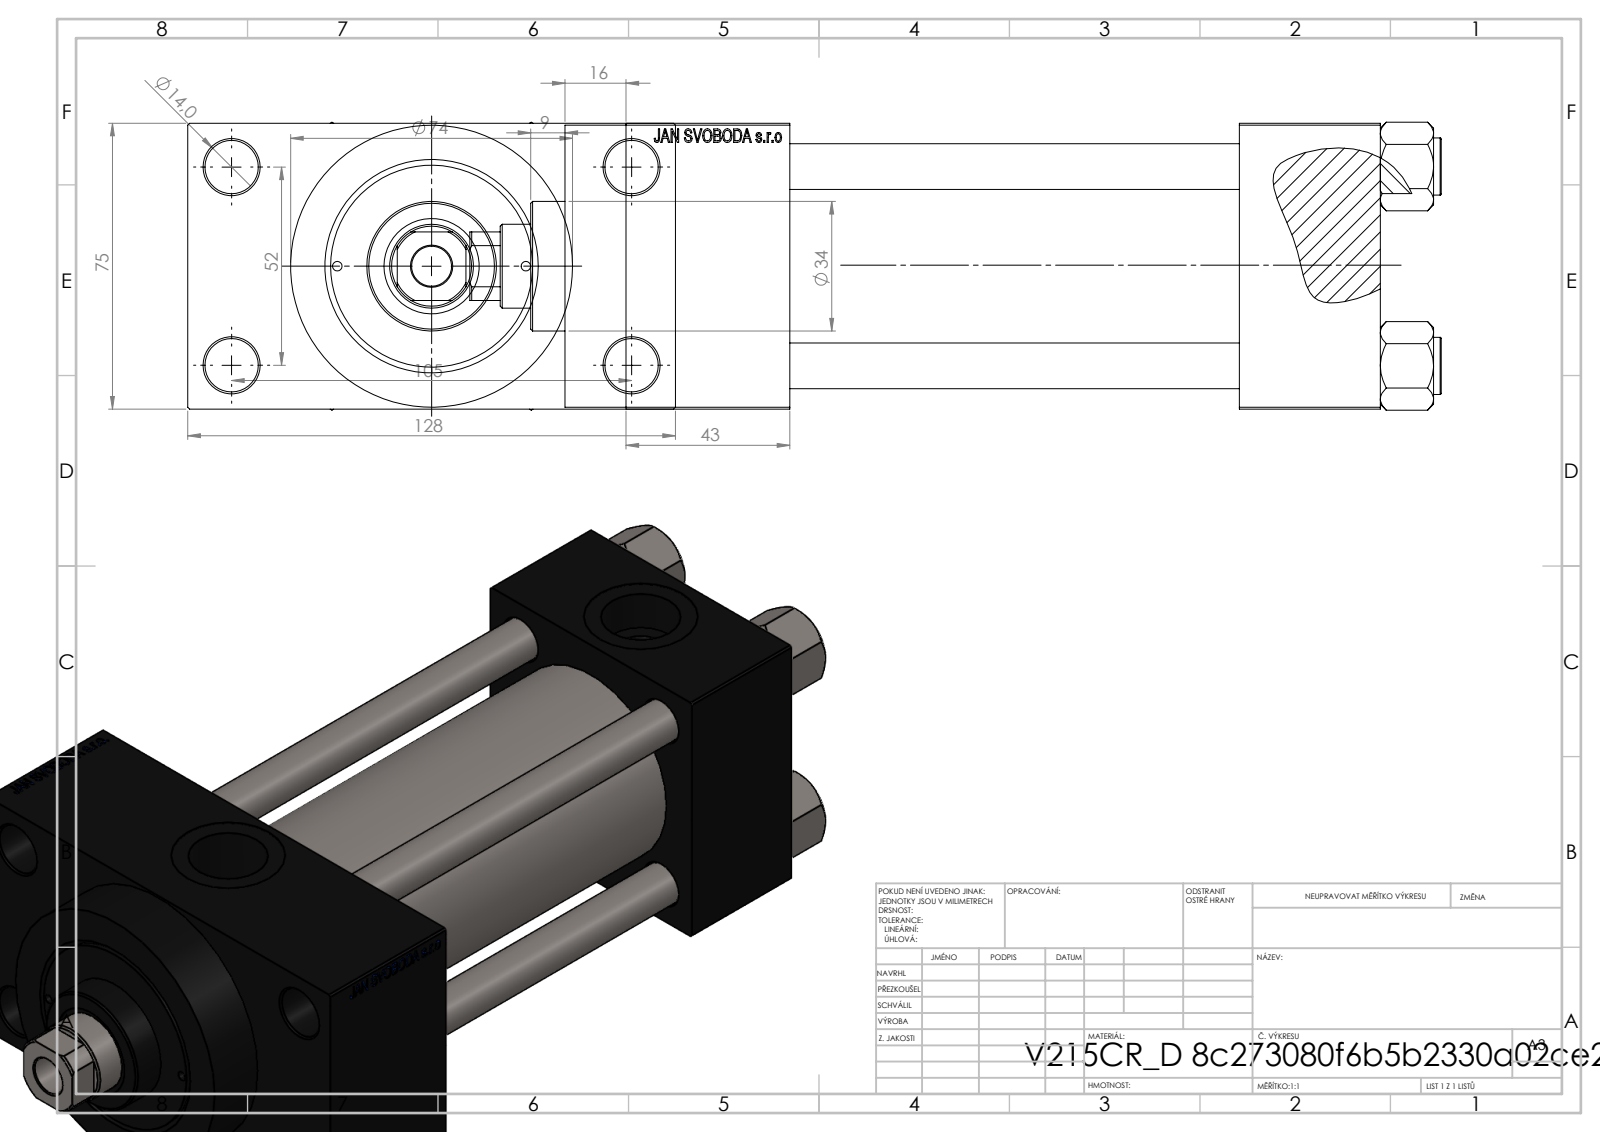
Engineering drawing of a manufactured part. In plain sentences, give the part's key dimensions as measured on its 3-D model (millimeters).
The part is named "V215CR_D_Body; V215CR_VCP_D; NUT_M5_D; V215_VC_A (+1 more)". Its 3-D file was written by "SolidWorks 2019 (CONFIG_CONTROL_DESIGN)". It is 11 solids with 1112 faces: 499 planar, 93 cylindrical and 520 other. Overall it measures 255 by 128 by 75.54 millimeters. Its volume is 886 222 cubic millimeters and its surface area 198 058 square millimeters. Round holes: 4 of diameter 12, 4 of diameter 14, 2 of diameter 2.5, 2 of diameter 7, 2 of diameter 20.96, 2 of diameter 30, 1 of diameter 10.5, 1 of diameter 22, 1 of diameter 25, 1 of diameter 41, 1 of diameter 50, 1 of diameter 53. Round bosses or shafts: 4 of diameter 15, 1 of diameter 74, 1 of diameter 56, 1 of diameter 34. Partial cylindrical surfaces (rounded edges, fillets, slot ends): 1 of radius 10.5. The main face-to-face distances are 75, 118, 37, 155, 26.5, 101.5, 198, 161, 43, 16. The hole center spacings are 26.19, 26.35, 36.98, 38.03, 52.3, 57.22, 58.43, 58.59.
